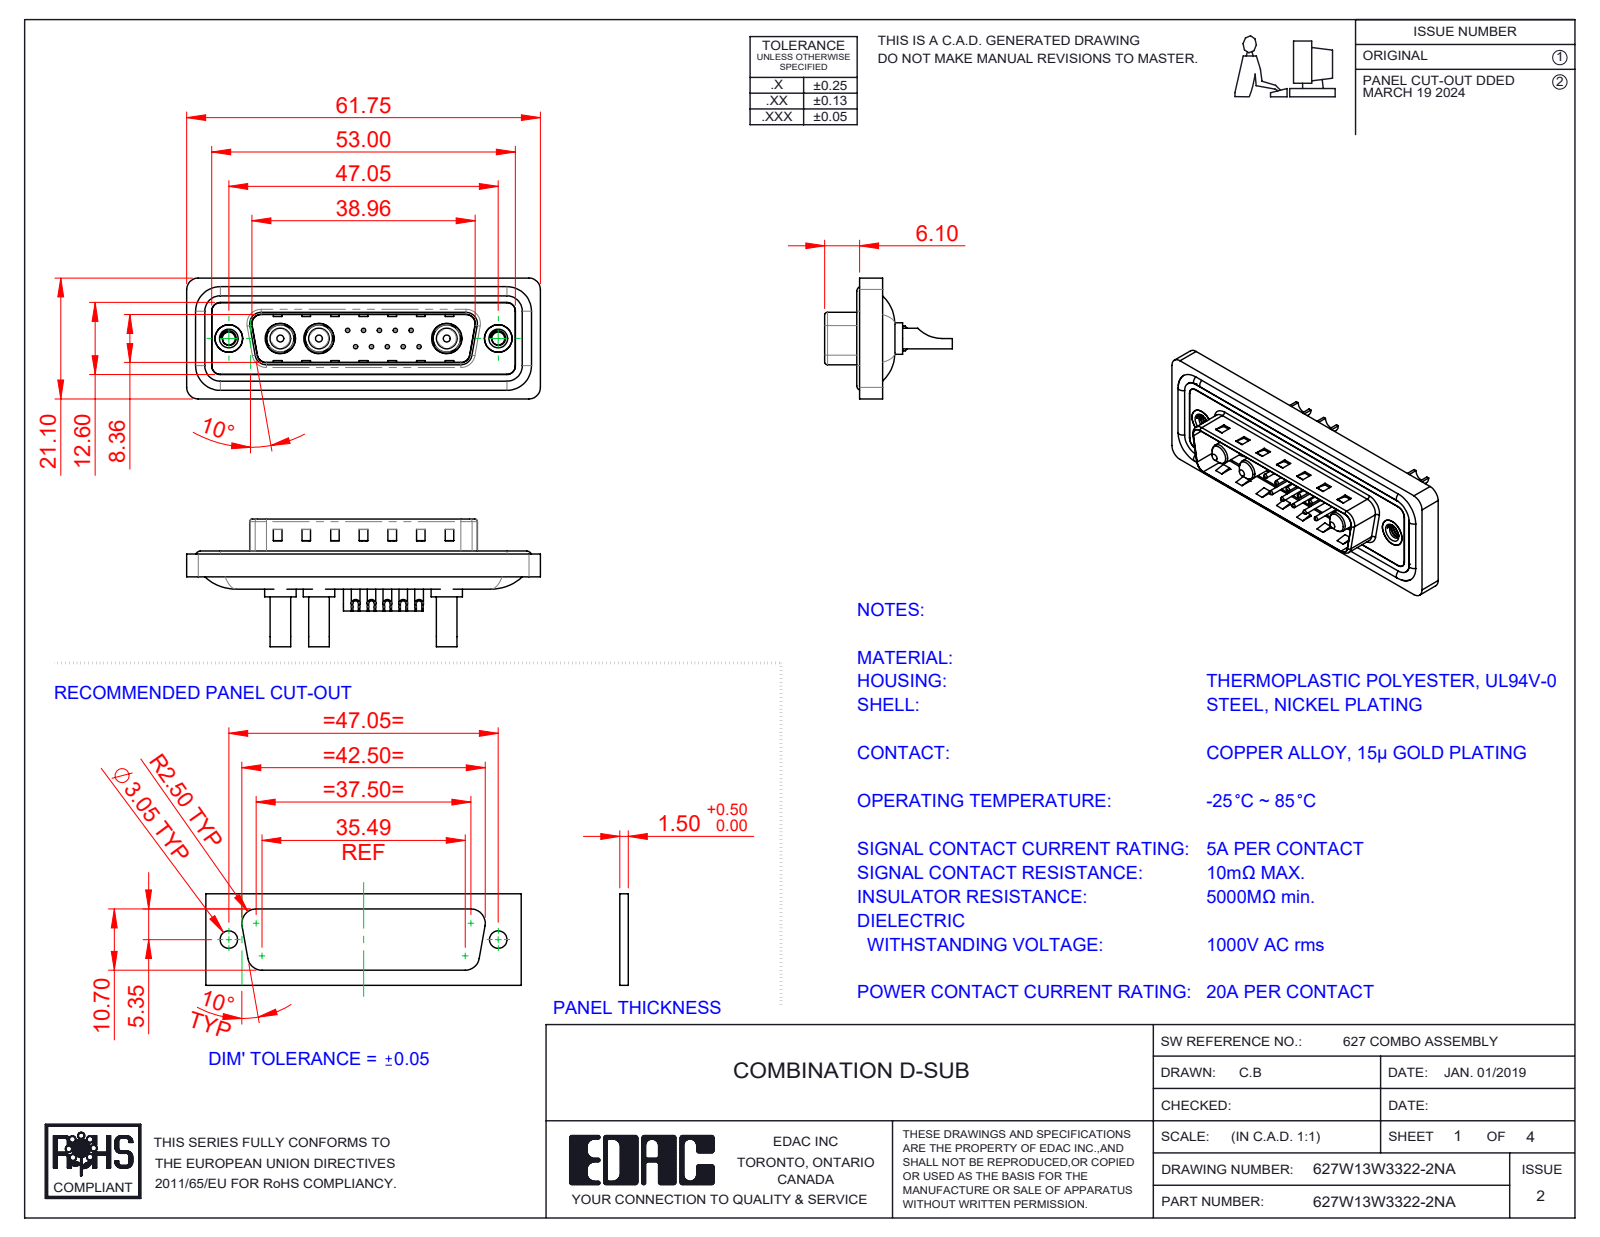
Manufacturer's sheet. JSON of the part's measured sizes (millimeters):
{"part_name": "627Combo Waterproof Housing_25 Contacts; 627Combo Shell Rear_25 Contacts; 627Combo Contact Row 1_22; 627Combo Contact Row 2_22 (+5 more)", "step_written_by": "SolidWorks 2023 (CONFIG_CONTROL_DESIGN)", "units": "millimeters", "bodies": {"solids": 23, "faces": 989, "planar": 338, "cylindrical": 416, "other": 235}, "overall_size": [61.75, 22.3, 21.1], "volume_mm3": 7391, "surface_area_mm2": 12199, "round_holes": [[0.75, 10], [1, 10], [1.6, 10], [2, 10], [2.7, 3], [4.85, 3], [5.3, 3], [2.26, 2], [4, 2], [4.8, 2], [5, 2]], "round_bosses_or_shafts": [[1.5, 10], [1.6, 4], [5.5, 3], [5.2, 3], [4.75, 3], [3.75, 3], [3.6, 3], [4.9, 2]], "partial_cylinders_radius": [[1.5, 22], [2, 18], [0.5, 8], [1.6, 8], [1, 6], [0.25, 4], [0.6, 4], [0.65, 4]], "face_to_face_distances": [0.4, 1.5, 1.1, 1.6, 0.5, 3.1, 2.9, 0.82, 9.58, 4.1], "hole_center_spacings": [3.16, 2.77, 5.04, 5.54, 7.49, 5.03, 8.31, 10.11]}
